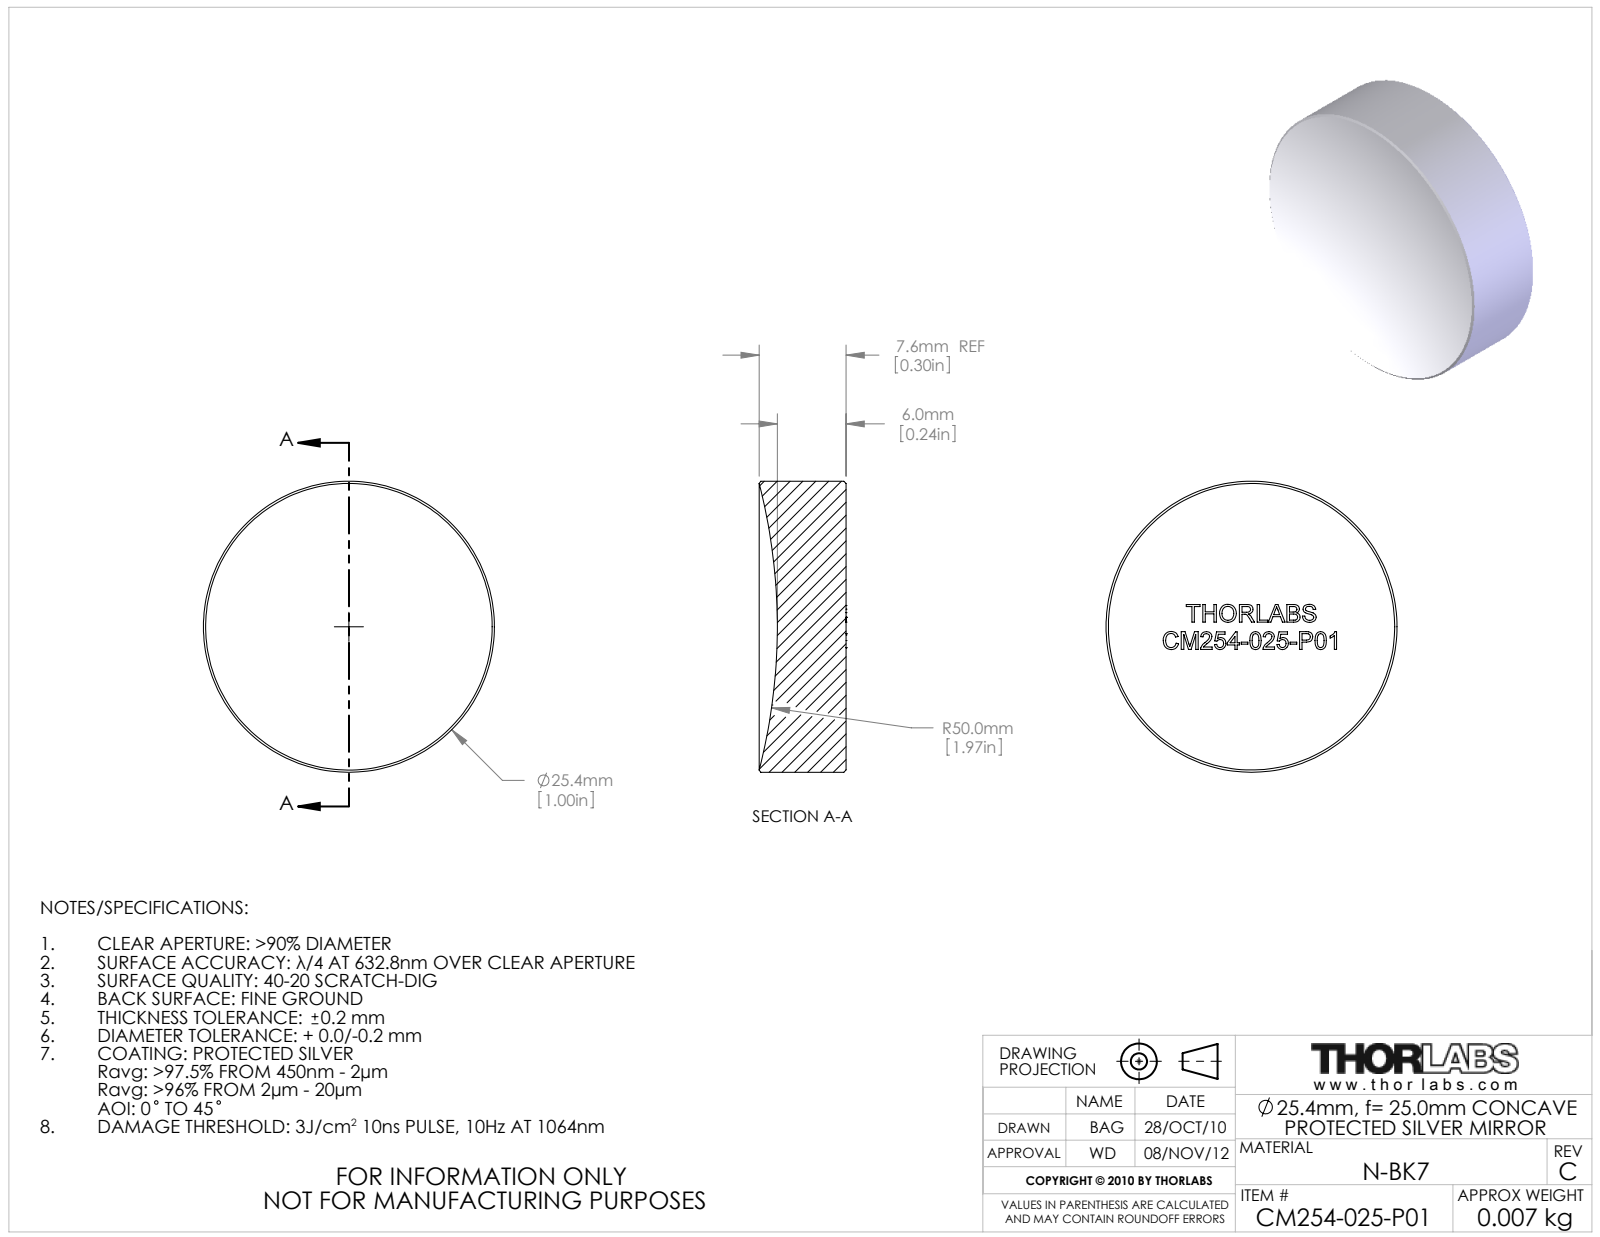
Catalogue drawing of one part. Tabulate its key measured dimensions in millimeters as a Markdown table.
| quantity | value |
| --- | --- |
| part name | 17567-E0W |
| STEP written by | SolidWorks 2009 (AUTOMOTIVE_DESIGN) |
| units | millimeters |
| bodies | 1 solid, 286 faces (162 planar, 2 cylindrical, 122 other) |
| overall size | 25.4 × 25.4 × 7.6 |
| volume | 3 460 mm³ |
| surface area | 1 610 mm² |
| round bosses / shafts (diameter × count) | 25.4 × 1 |
| main face-to-face distances | 1.5, 1.9, 2.4, 1.4, 1.3, 0.9, 2.4, 4.1, 5.4, 0.7 |
